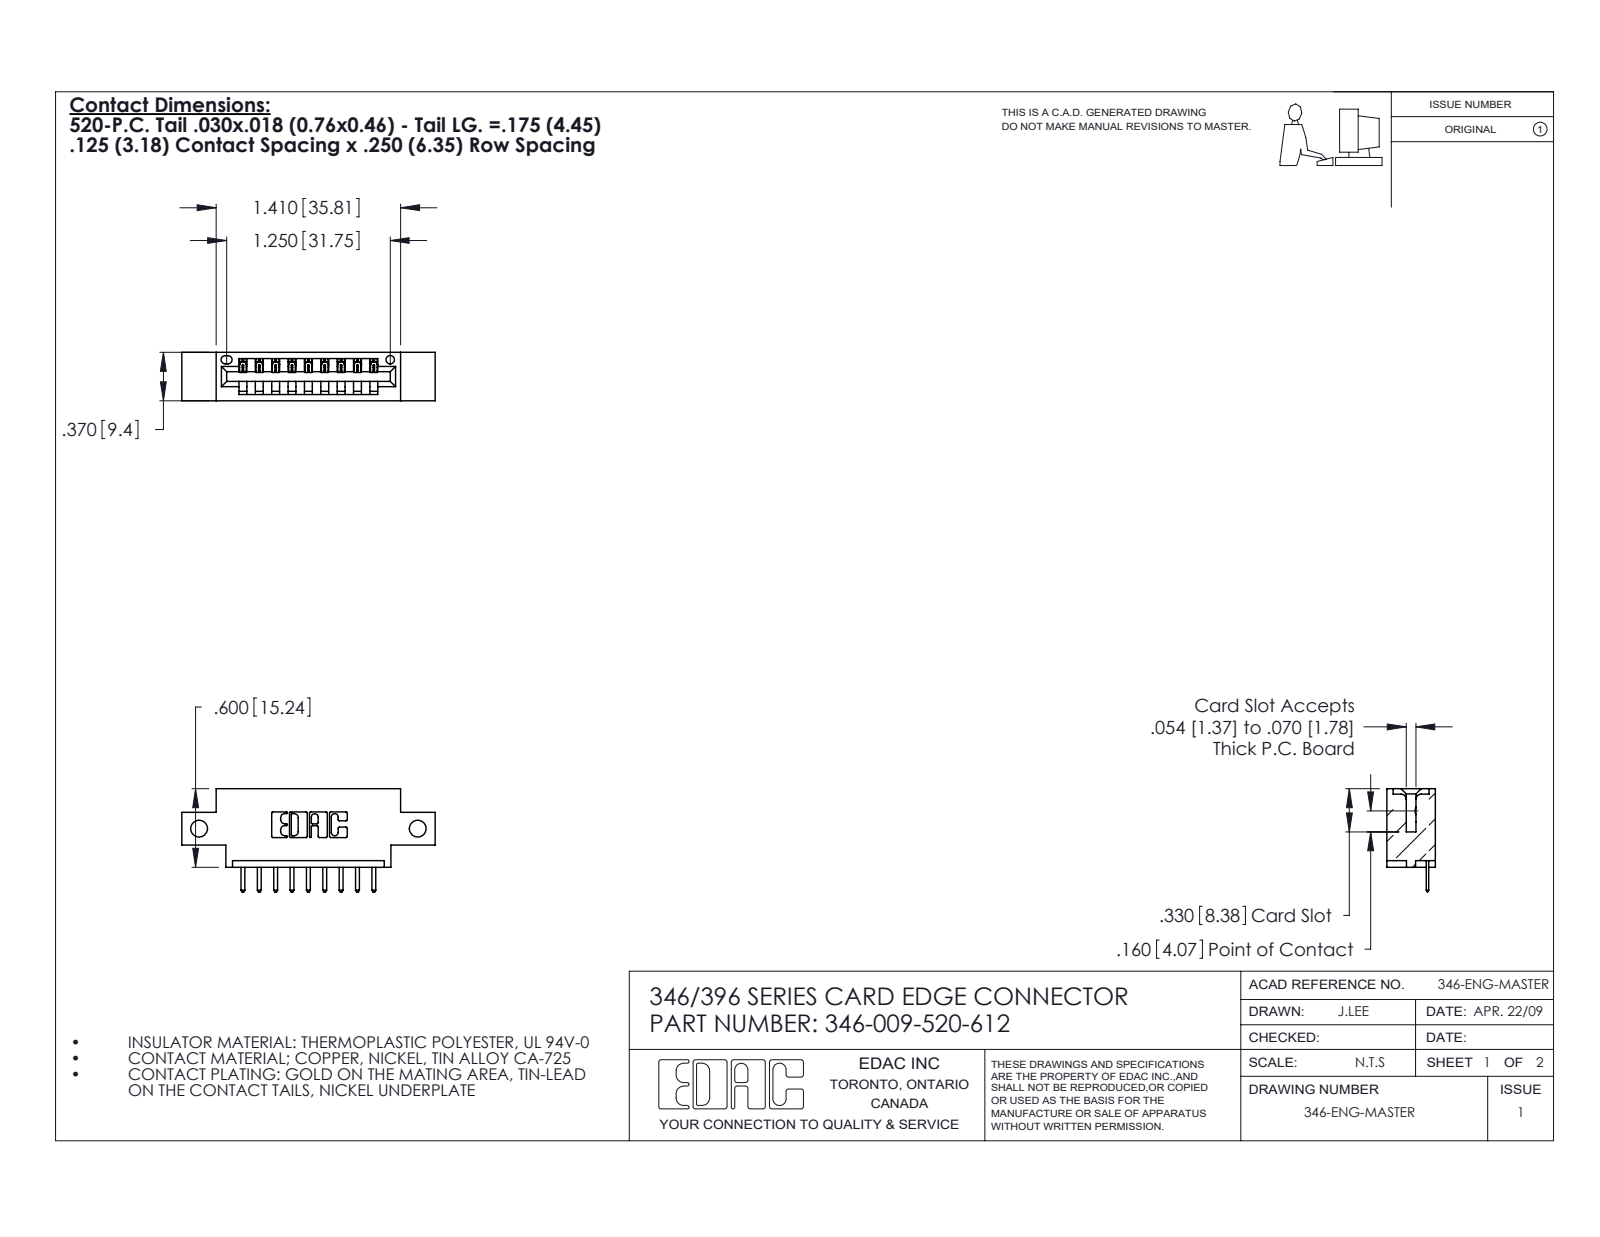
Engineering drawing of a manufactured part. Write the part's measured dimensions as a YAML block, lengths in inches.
part_name: "346 Part_0.170 Offset - Side Mount; 345-292-001_345-293-120; 346-009-520-612"
step_written_by: "SolidWorks 2020 (CONFIG_CONTROL_DESIGN)"
units: inches
bodies: {solids: 10, faces: 684, planar: 458, cylindrical: 226, other: 0}
overall_size: [1.935, 0.788, 0.37]
volume: 0.257
surface_area: 7.492
round_holes:
  - {diameter: 0.128, count: 2}
  - {diameter: 0.064, count: 1}
partial_cylinders:
  - {radius: 0.01, count: 22}
  - {radius: 0.01, count: 20}
  - {radius: 0.006, count: 18}
  - {radius: 0.007, count: 6}
  - {radius: 0.031, count: 6}
  - {radius: 0.026, count: 3}
  - {radius: 0.031, count: 2}
  - {radius: 0.04, count: 2}
face_to_face_distances: [0.25, 0.37, 0.048, 0.322, 0.148, 0.222, 0.1, 0.174, 0.072, 0.298]
hole_center_spacings: [1.67]
